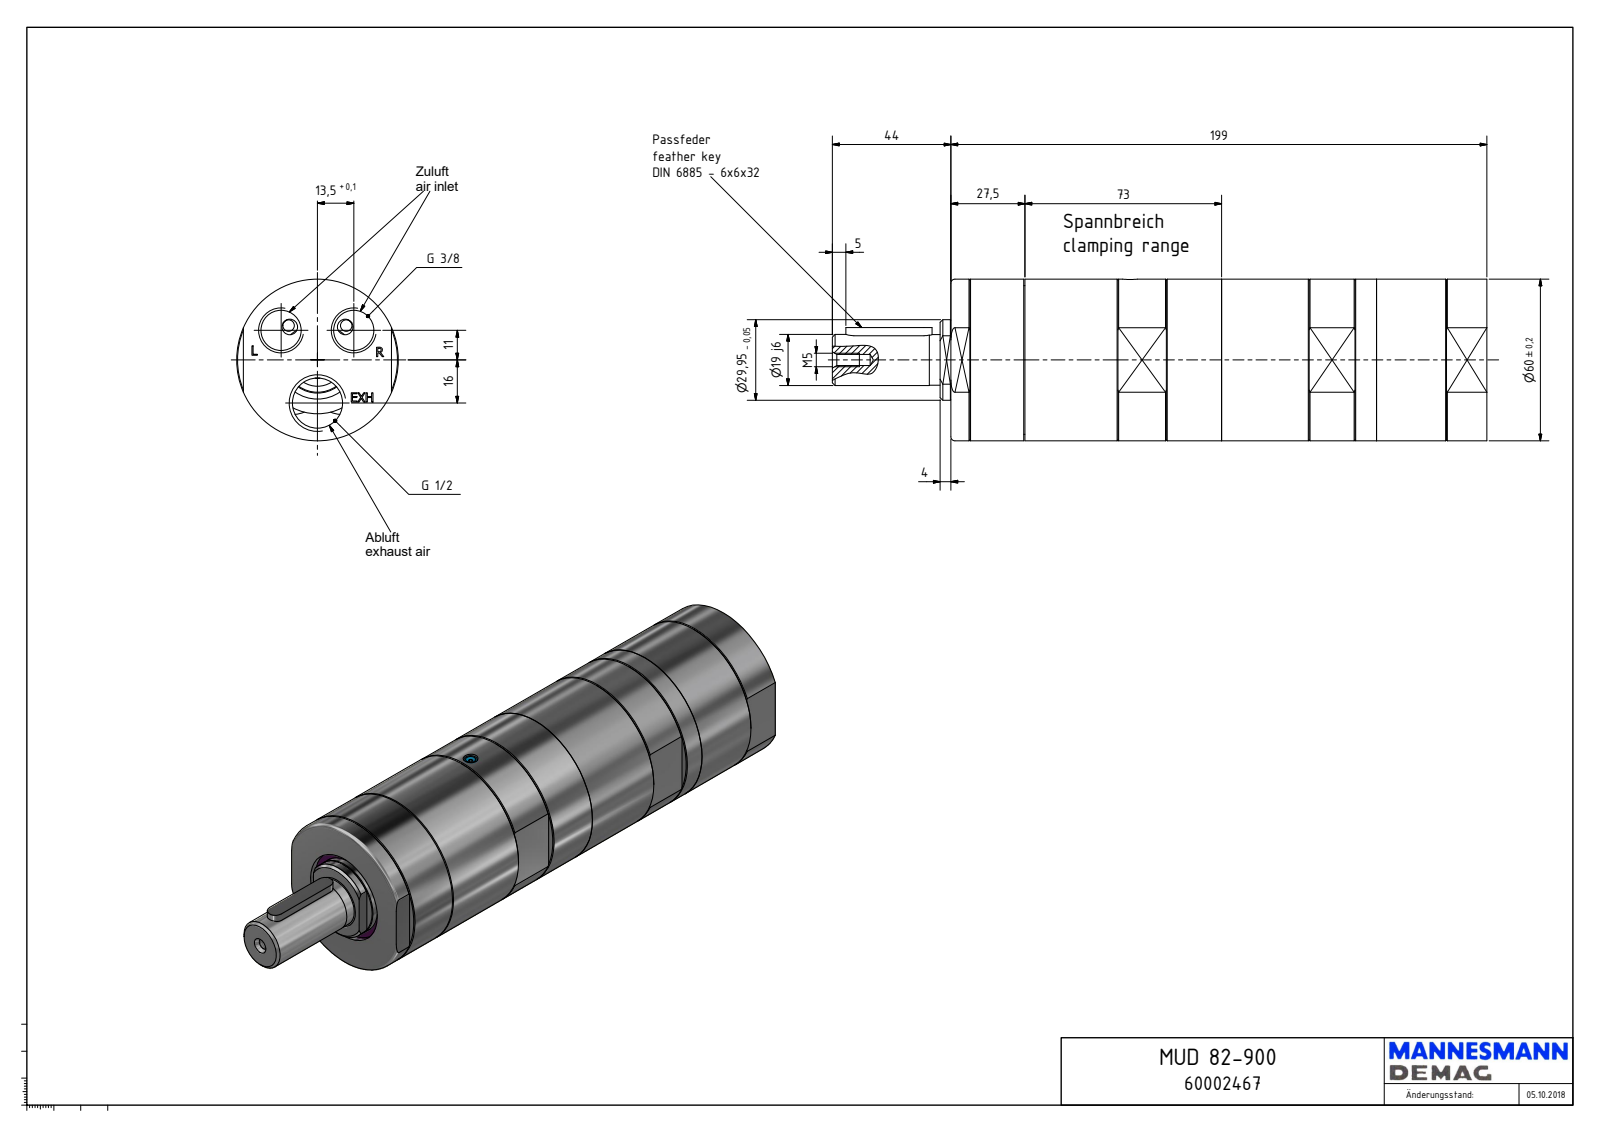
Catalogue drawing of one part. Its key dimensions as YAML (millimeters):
part_name: "MUD 82-425_60002467"
step_written_by: "Autodesk Inventor 2018 (AUTOMOTIVE_DESIGN)"
units: millimeters
bodies: {solids: 1, faces: 202, planar: 109, cylindrical: 45, other: 48}
overall_size: [243, 60, 60]
volume: 558407
surface_area: 53006
round_holes:
  - {diameter: 14.95, count: 2}
  - {diameter: 1.55, count: 1}
  - {diameter: 4, count: 1}
  - {diameter: 4.13, count: 1}
  - {diameter: 5.5, count: 1}
  - {diameter: 18.63, count: 1}
  - {diameter: 35, count: 1}
  - {diameter: 40, count: 1}
  - {diameter: 55.38, count: 1}
round_bosses_or_shafts:
  - {diameter: 60, count: 1}
  - {diameter: 55.18, count: 1}
  - {diameter: 29.95, count: 1}
  - {diameter: 19, count: 1}
  - {diameter: 18.8, count: 1}
  - {diameter: 5, count: 1}
  - {diameter: 3.6, count: 1}
partial_cylinders:
  - {radius: 3, count: 2}
  - {radius: 7.5, count: 2}
  - {radius: 8.5, count: 1}
  - {radius: 19.51, count: 1}
  - {radius: 23.5, count: 1}
  - {radius: 25.58, count: 1}
face_to_face_distances: [199, 55, 182.82, 16.18, 186, 3.18, 13, 158.5, 27.5, 155.32]
hole_center_spacings: [17.41, 30.19, 16, 27]
